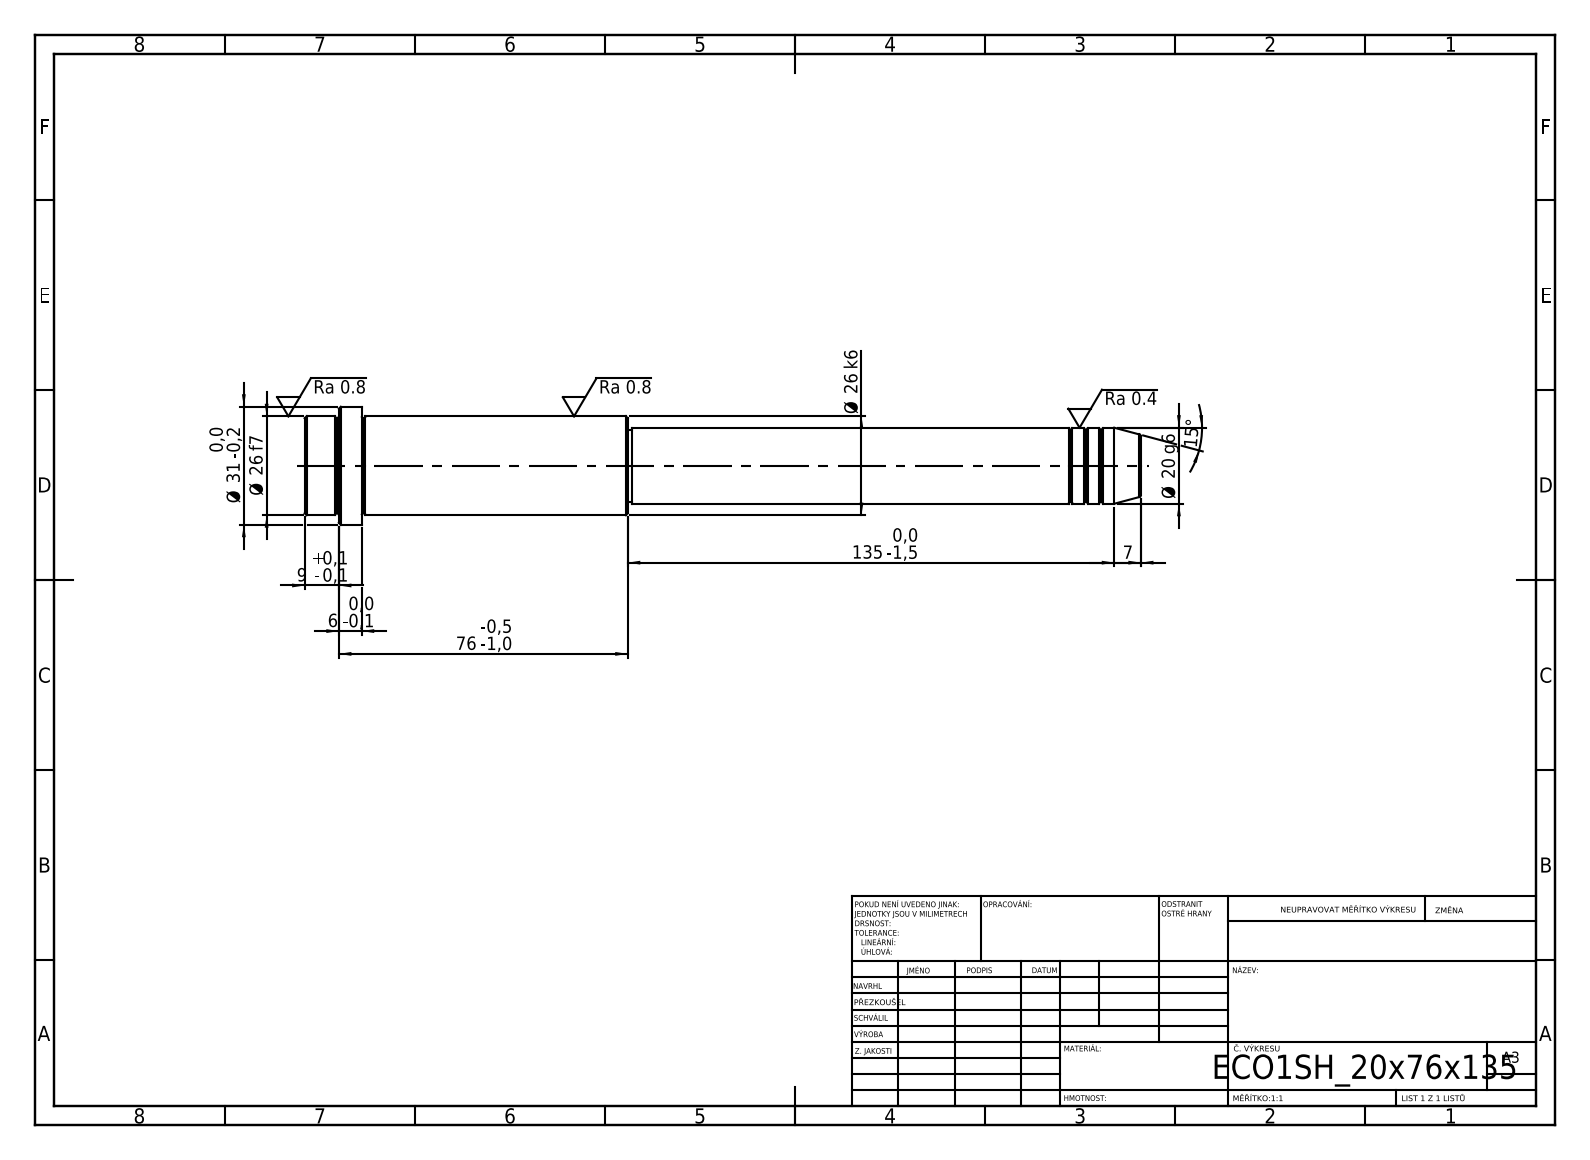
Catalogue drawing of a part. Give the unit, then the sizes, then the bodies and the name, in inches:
Units: inches
Overall size (bounding box): 8.661 × 1.22 × 1.22
Round bosses / shafts (diameter × count): ⌀1.22 ×1, ⌀1.024 ×1, ⌀0.787 ×1, ⌀0.748 ×1
Main face-to-face distances: 0.591, 2.756, 3.346, 5.315, 8.071, 8.661, 8.307, 2.992, 0.236, 0.354
Volume: 5.388 in³ · Surface area: 26.44 in²
Bodies: 1 solid, 52 faces (6 planar, 16 cylindrical, 30 other)
STEP written by: SolidWorks 2019 (CONFIG_CONTROL_DESIGN)
